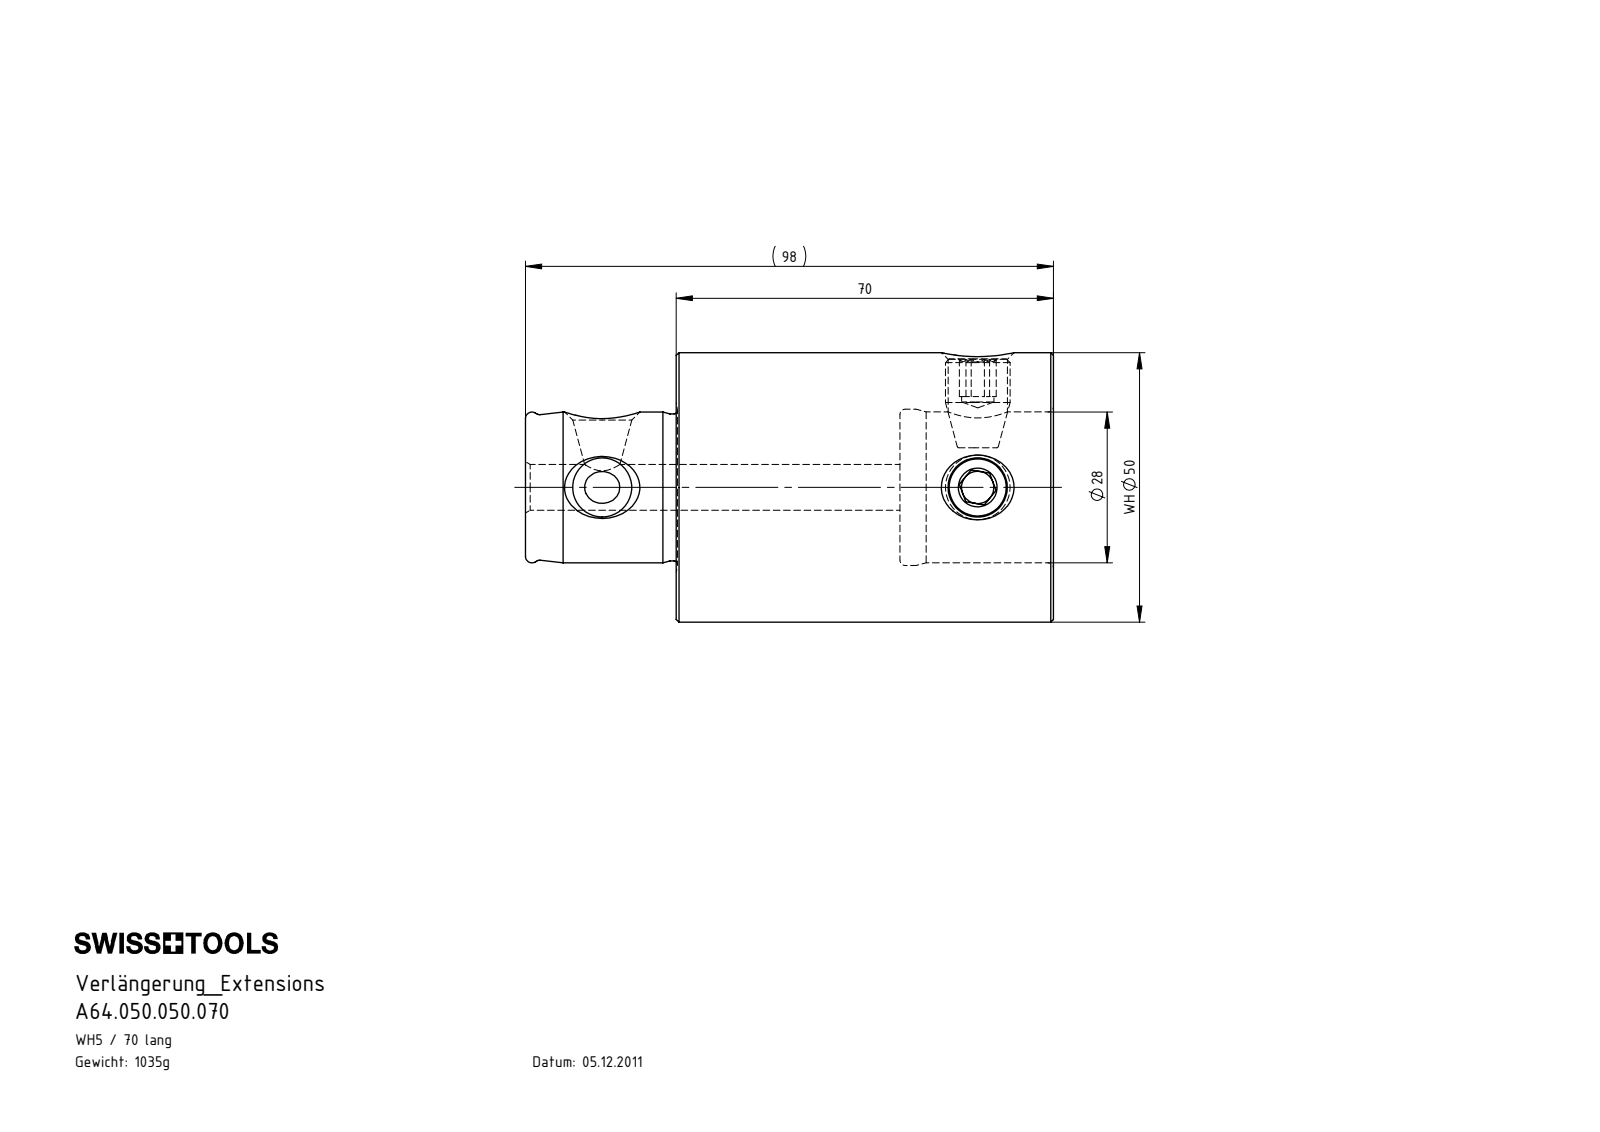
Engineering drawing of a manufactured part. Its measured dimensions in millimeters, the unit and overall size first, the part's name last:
Units: millimetres
Overall size (bounding box): 98 × 50 × 50
Round holes (diameter × count): ⌀11 ×2, ⌀8.5 ×1, ⌀28 ×1, ⌀29 ×1
Round bosses / shafts (diameter × count): ⌀12 ×2, ⌀50 ×1, ⌀27.3 ×1
Main face-to-face distances: 70, 41.5, 28.5, 28, 69.5, 98, 6, 16.5, 9.5, 7
Volume: 131 973 mm³ · Surface area: 23 873 mm²
Bodies: 3 solids, 94 faces (22 planar, 20 cylindrical, 52 other)
Part name (STEP PRODUCT): WH5-ER1.001.017; WH5-WH5.001.070; WH5-WH5.001.070_A
STEP written by: SolidWorks 2015 (AUTOMOTIVE_DESIGN)
